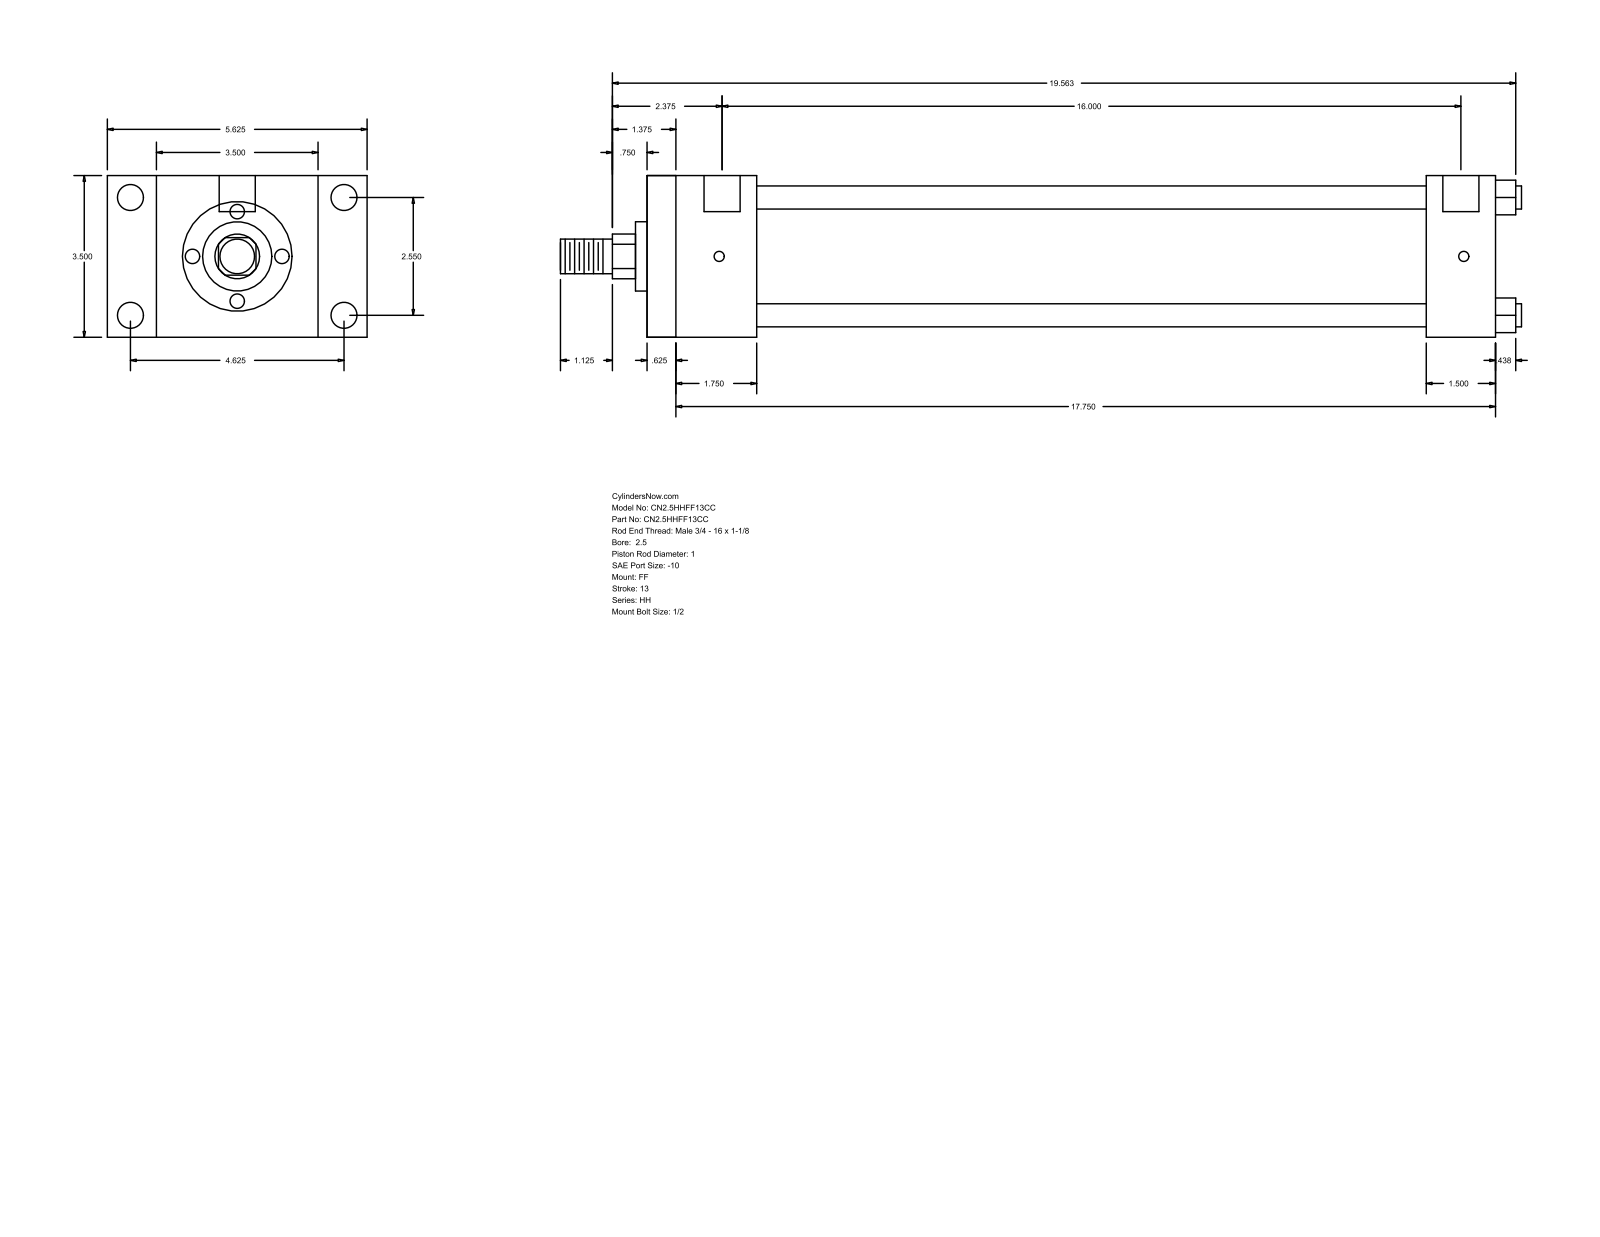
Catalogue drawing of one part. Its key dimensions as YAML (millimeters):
part_name: "HH_FF__0250_1"
step_written_by: "GSSL Pune (CONFIG_CONTROL_DESIGN)"
units: millimeters
bodies: {solids: 0, faces: 92, planar: 64, cylindrical: 28, other: 0}
overall_size: [528.64, 142.88, 88.9]
round_holes:
  - {diameter: 5.56, count: 4}
  - {diameter: 14.3, count: 4}
  - {diameter: 19.84, count: 2}
round_bosses_or_shafts:
  - {diameter: 12.7, count: 4}
  - {diameter: 73.03, count: 1}
  - {diameter: 38.1, count: 1}
  - {diameter: 25.4, count: 1}
  - {diameter: 19.05, count: 1}
partial_cylinders:
  - {radius: 12.29, count: 1}
face_to_face_distances: [88.9, 466.72, 15.87, 450.85, 60.33, 44.46, 406.39, 428.63, 412.76, 368.3]
hole_center_spacings: [64.76, 117.48, 134.15, 409.57, 1.58, 1.59, 406.4, 407.98]
